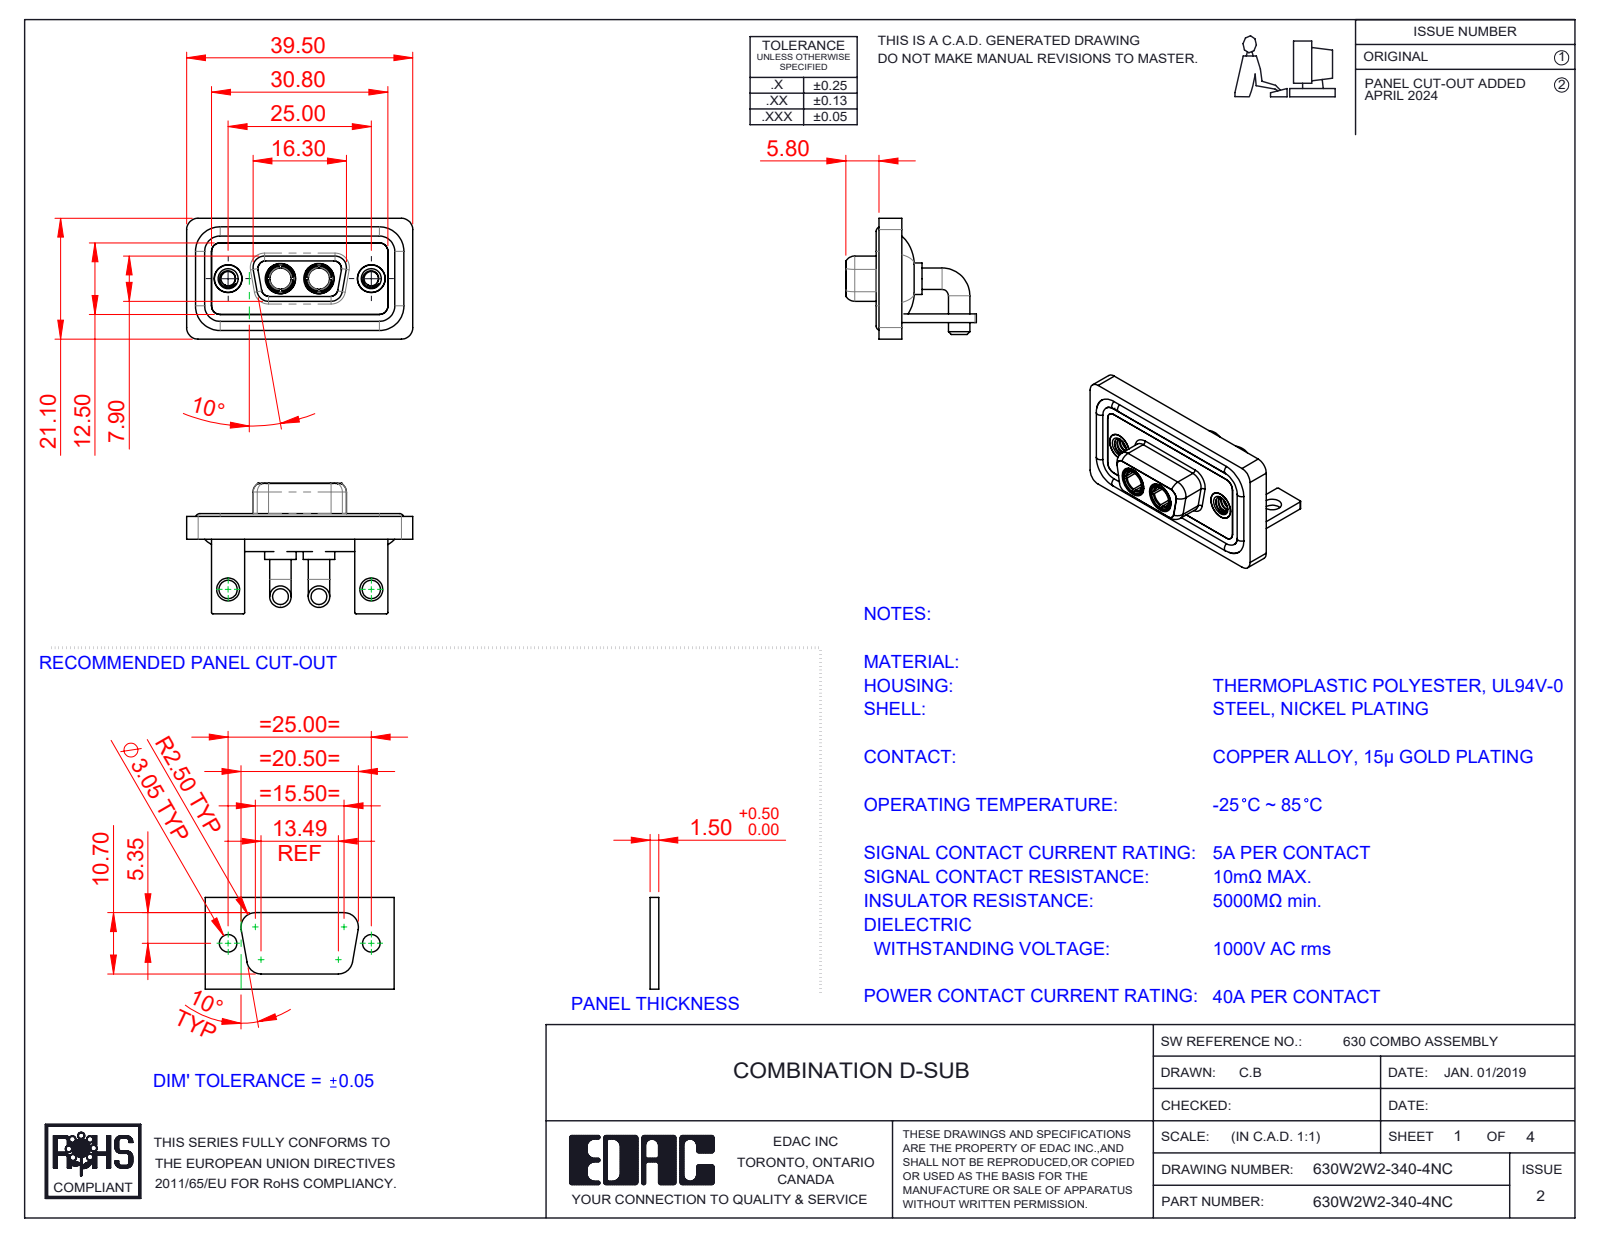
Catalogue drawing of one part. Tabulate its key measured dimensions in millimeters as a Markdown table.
| quantity | value |
| --- | --- |
| part name | 630Combo Waterproof Housing_09 Contacts; 630Combo Shell Front_09 Contacts; 630Combo Threaded Rivet_A; 630Combo Stabilizer Bracket_50 Contacts (+4 more) |
| STEP written by | SolidWorks 2023 (CONFIG_CONTROL_DESIGN) |
| units | millimeters |
| bodies | 13 solids, 584 faces (183 planar, 260 cylindrical, 141 other) |
| overall size | 39.5 × 22.8 × 21.1 |
| volume | 5 321 mm³ |
| surface area | 8 612 mm² |
| round holes (diameter × count) | 4.85 × 4, 2.5 × 2, 3.2 × 2, 3.7 × 2, 4 × 2, 4.05 × 2, 5 × 2, 5.3 × 2 |
| round bosses / shafts (diameter × count) | 3.75 × 4, 1.6 × 4, 5.5 × 2, 5.2 × 2, 4.96 × 2, 4.95 × 2, 4.8 × 2, 4.75 × 2 |
| partial cylindrical surfaces (radius × count) | 2 × 19, 1.5 × 18, 0.25 × 16, 1.35 × 8, 1.6 × 8, 0.5 × 5, 0.6 × 4, 0.65 × 4 |
| main face-to-face distances | 0.4, 2.9, 1.5, 1.8, 1.1, 3.7, 0.8, 2.5, 1.6, 3.1 |
| hole center spacings | 9.14, 15.86, 25, 6.72 |
